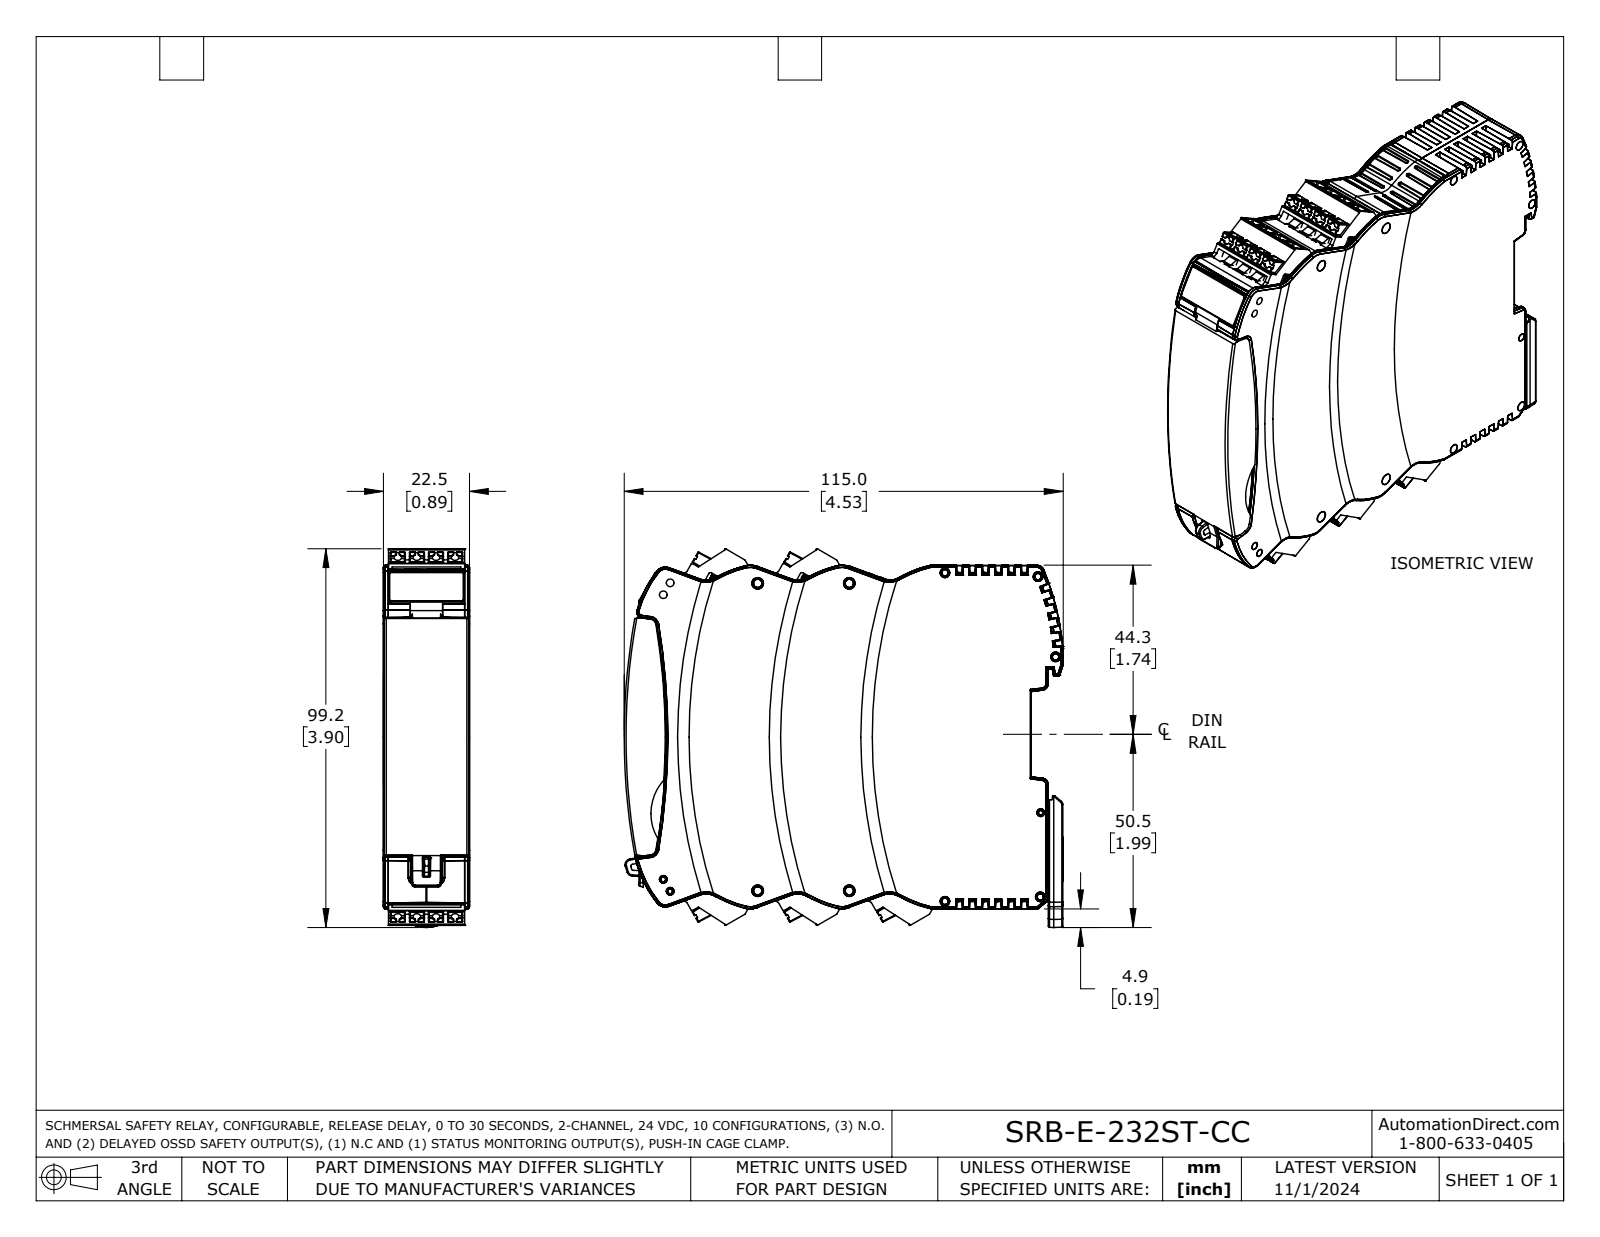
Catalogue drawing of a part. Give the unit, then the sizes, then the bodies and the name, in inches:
Units: inches
Overall size (bounding box): 4.528 × 3.904 × 0.886
Round bosses / shafts (diameter × count): ⌀0.067 ×1
Partial cylindrical surfaces — rounded edges, fillets, slot ends (radius × count): R0.008 ×260, R0.012 ×249, R0.02 ×211, R0.01 ×60, R0.004 ×55, R0.039 ×36, R0.059 ×26, R0.047 ×20
Main face-to-face distances: 0.886, 0.133, 0.267, 0.035, 0.177, 0.05, 0.785, 0.134, 0.05, 0.85
Volume: 12.97 in³ · Surface area: 68.71 in²
Bodies: 2 solids, 5368 faces (3063 planar, 1431 cylindrical, 874 other)
Part name (STEP PRODUCT): SRB-E-232ST-CC
STEP written by: SolidWorks 2023 (AUTOMOTIVE_DESIGN)
